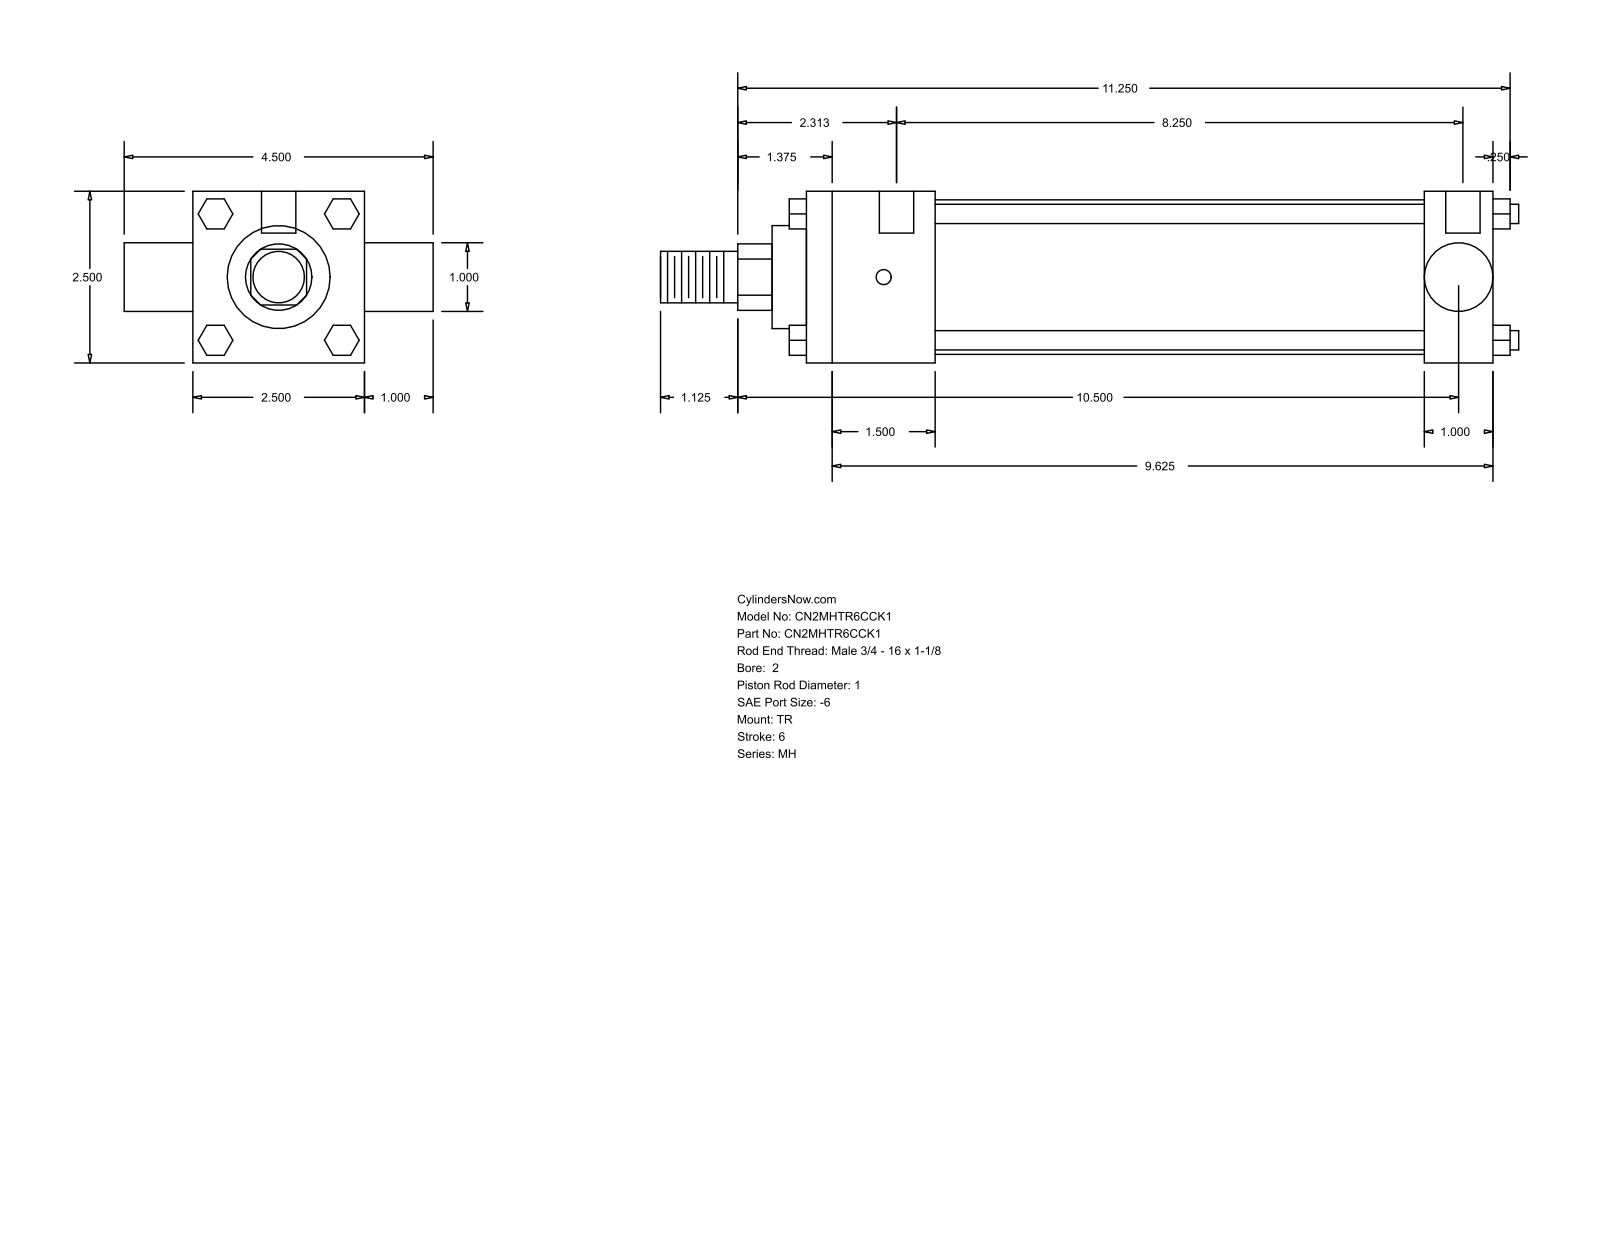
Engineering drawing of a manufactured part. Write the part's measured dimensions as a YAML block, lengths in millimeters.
part_name: "MH_TR__0200_1"
step_written_by: "GSSL Pune (CONFIG_CONTROL_DESIGN)"
units: millimeters
bodies: {solids: 0, faces: 120, planar: 92, cylindrical: 28, other: 0}
overall_size: [317.5, 114.3, 63.5]
round_holes:
  - {diameter: 5.56, count: 3}
  - {diameter: 12.7, count: 2}
round_bosses_or_shafts:
  - {diameter: 7.14, count: 4}
  - {diameter: 57.15, count: 1}
  - {diameter: 38.1, count: 1}
  - {diameter: 25.4, count: 1}
  - {diameter: 25.35, count: 1}
  - {diameter: 19.05, count: 1}
partial_cylinders:
  - {radius: 12.29, count: 1}
face_to_face_distances: [63.5, 254, 25.4, 47.63, 228.6, 180.97, 206.37, 88.9, 266.7, 6.35]
hole_center_spacings: [3.17, 4.76, 209.55, 212.72, 214.31, 217.48]
